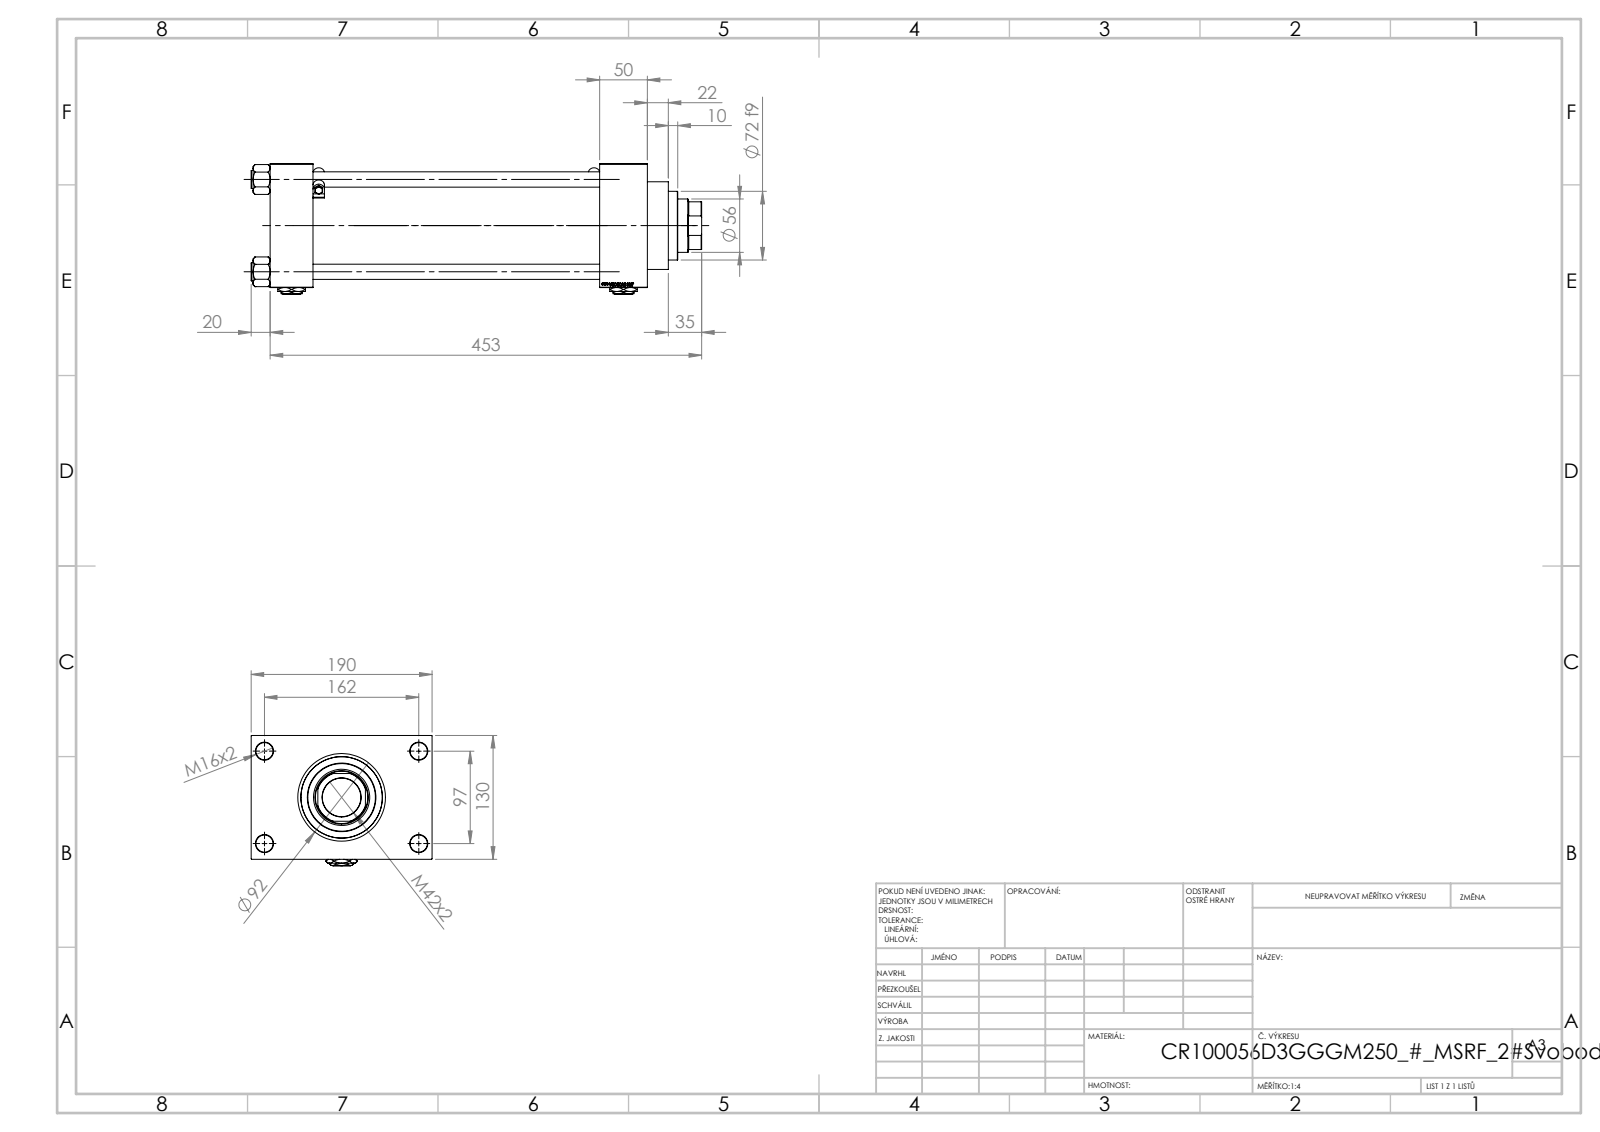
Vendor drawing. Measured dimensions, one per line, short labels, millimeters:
name: Zatka_pro_OIL_PORT; V215CR_D_Body; V215CR_VCP_D; NUT_M5_D (+3 more)
written by: SolidWorks 2019 (CONFIG_CONTROL_DESIGN)
unit: mm
bodies: 15 solids, 1317 faces (629 planar, 128 cylindrical, 560 other)
size: 473 × 190 × 137
volume: 3 613 000 mm³; area: 607 064 mm²
holes: 4× ⌀16, 4× ⌀18, 2× ⌀7, 2× ⌀26.44, 2× ⌀35, 1× ⌀40.5, 1× ⌀56, 1× ⌀59, 1× ⌀76, 1× ⌀85.5, 1× ⌀100
bosses: 4× ⌀19, 2× ⌀5, 2× ⌀2.5, 1× ⌀106, 1× ⌀92, 1× ⌀72
rounds: 12× R0.5, 4× R6, 1× R27
face distances: 130, 50, 45, 346, 301, 396, 351, 30, 160, 190
hole spacings: 32.55, 68.52, 94.41, 96.9, 102.27, 129.45, 161.73, 97
